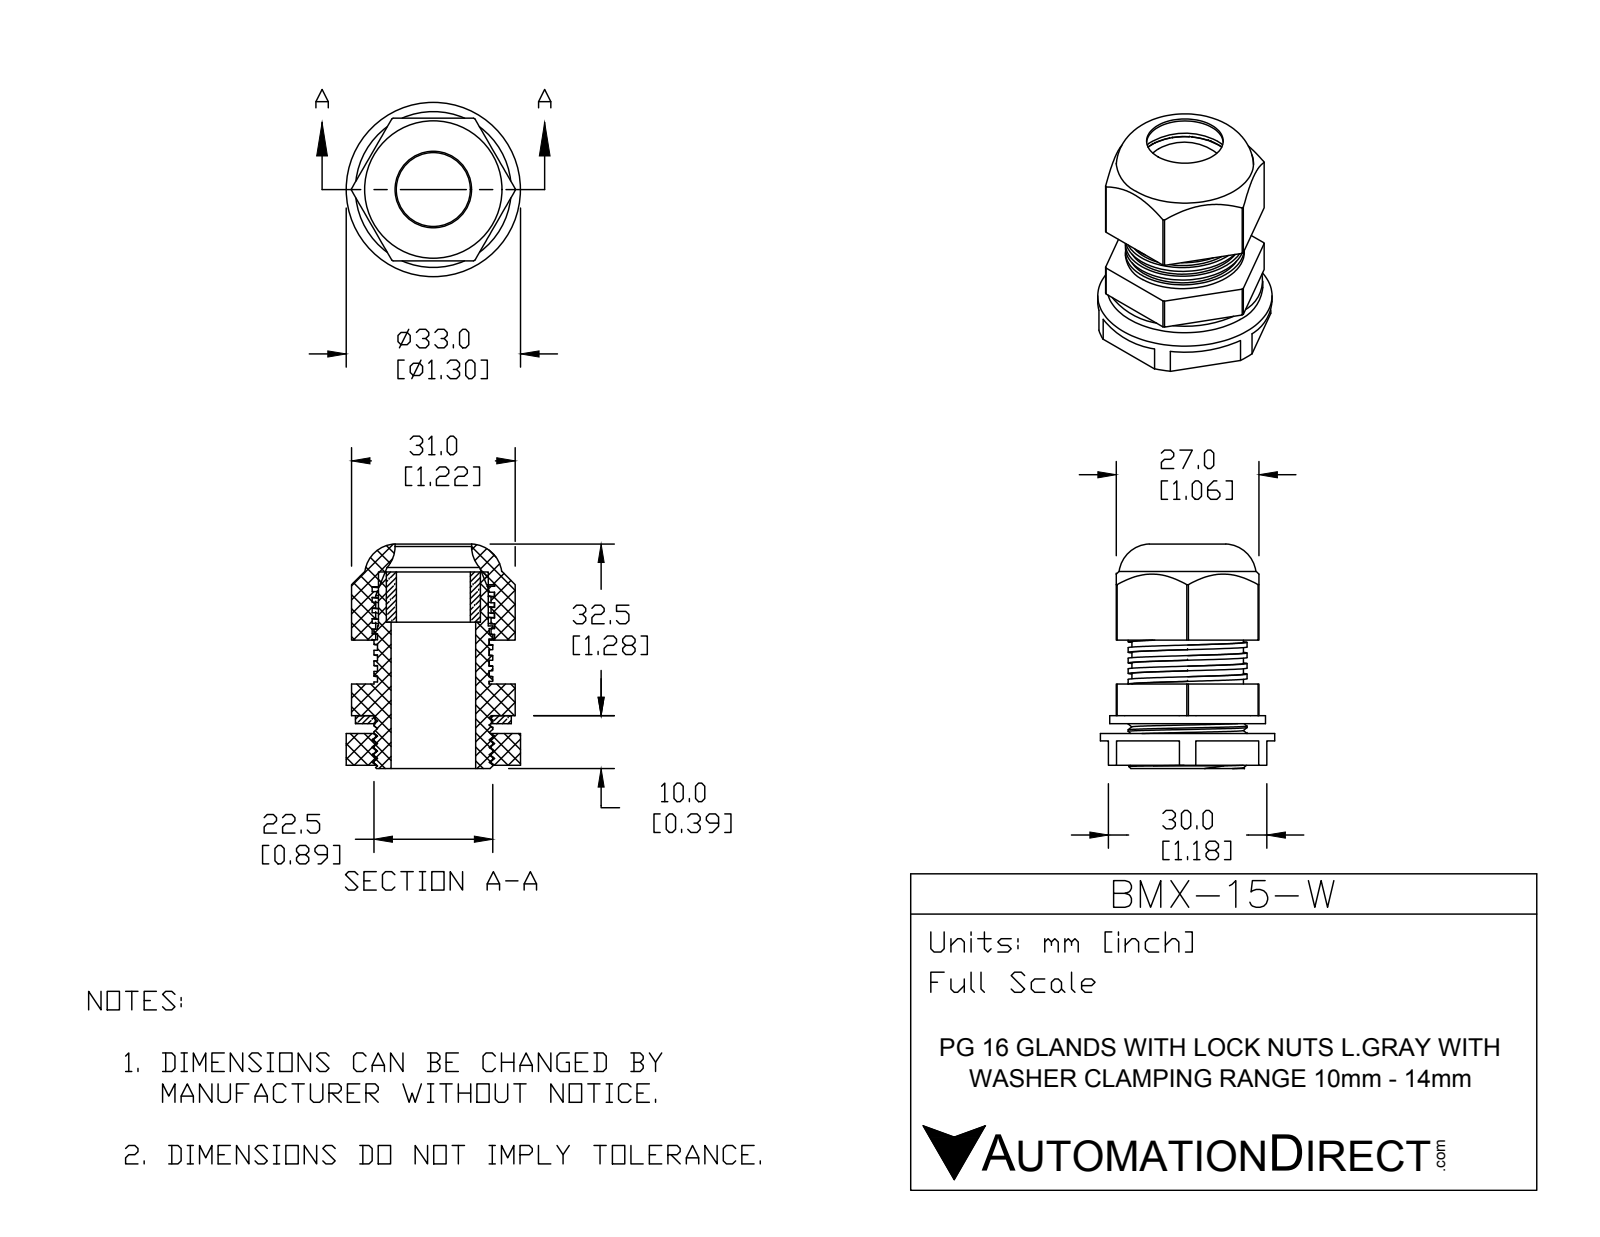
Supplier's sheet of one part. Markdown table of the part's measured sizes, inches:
| quantity | value |
| --- | --- |
| part name | BMX-15-W |
| STEP written by | SolidWorks 2015 (CONFIG_CONTROL_DESIGN) |
| units | inches |
| bodies | 5 solids, 205 faces (99 planar, 82 cylindrical, 24 other) |
| overall size | 1.673 × 1.299 × 1.299 |
| volume | 0.935 in³ |
| surface area | 22.56 in² |
| round holes (diameter × count) | 0.551 × 1, 0.571 × 1, 0.63 × 1, 0.701 × 1, 0.859 × 1, 0.866 × 1, 1.024 × 1 |
| round bosses / shafts (diameter × count) | 1.299 × 1, 1.161 × 1, 0.886 × 1, 0.819 × 1 |
| partial cylindrical surfaces (radius × count) | 0.61 × 1 |
| main face-to-face distances | 1.063, 0.059, 0.236, 0.369, 0.133, 1.122, 0.31, 0.074, 0.606, 0.295 |
